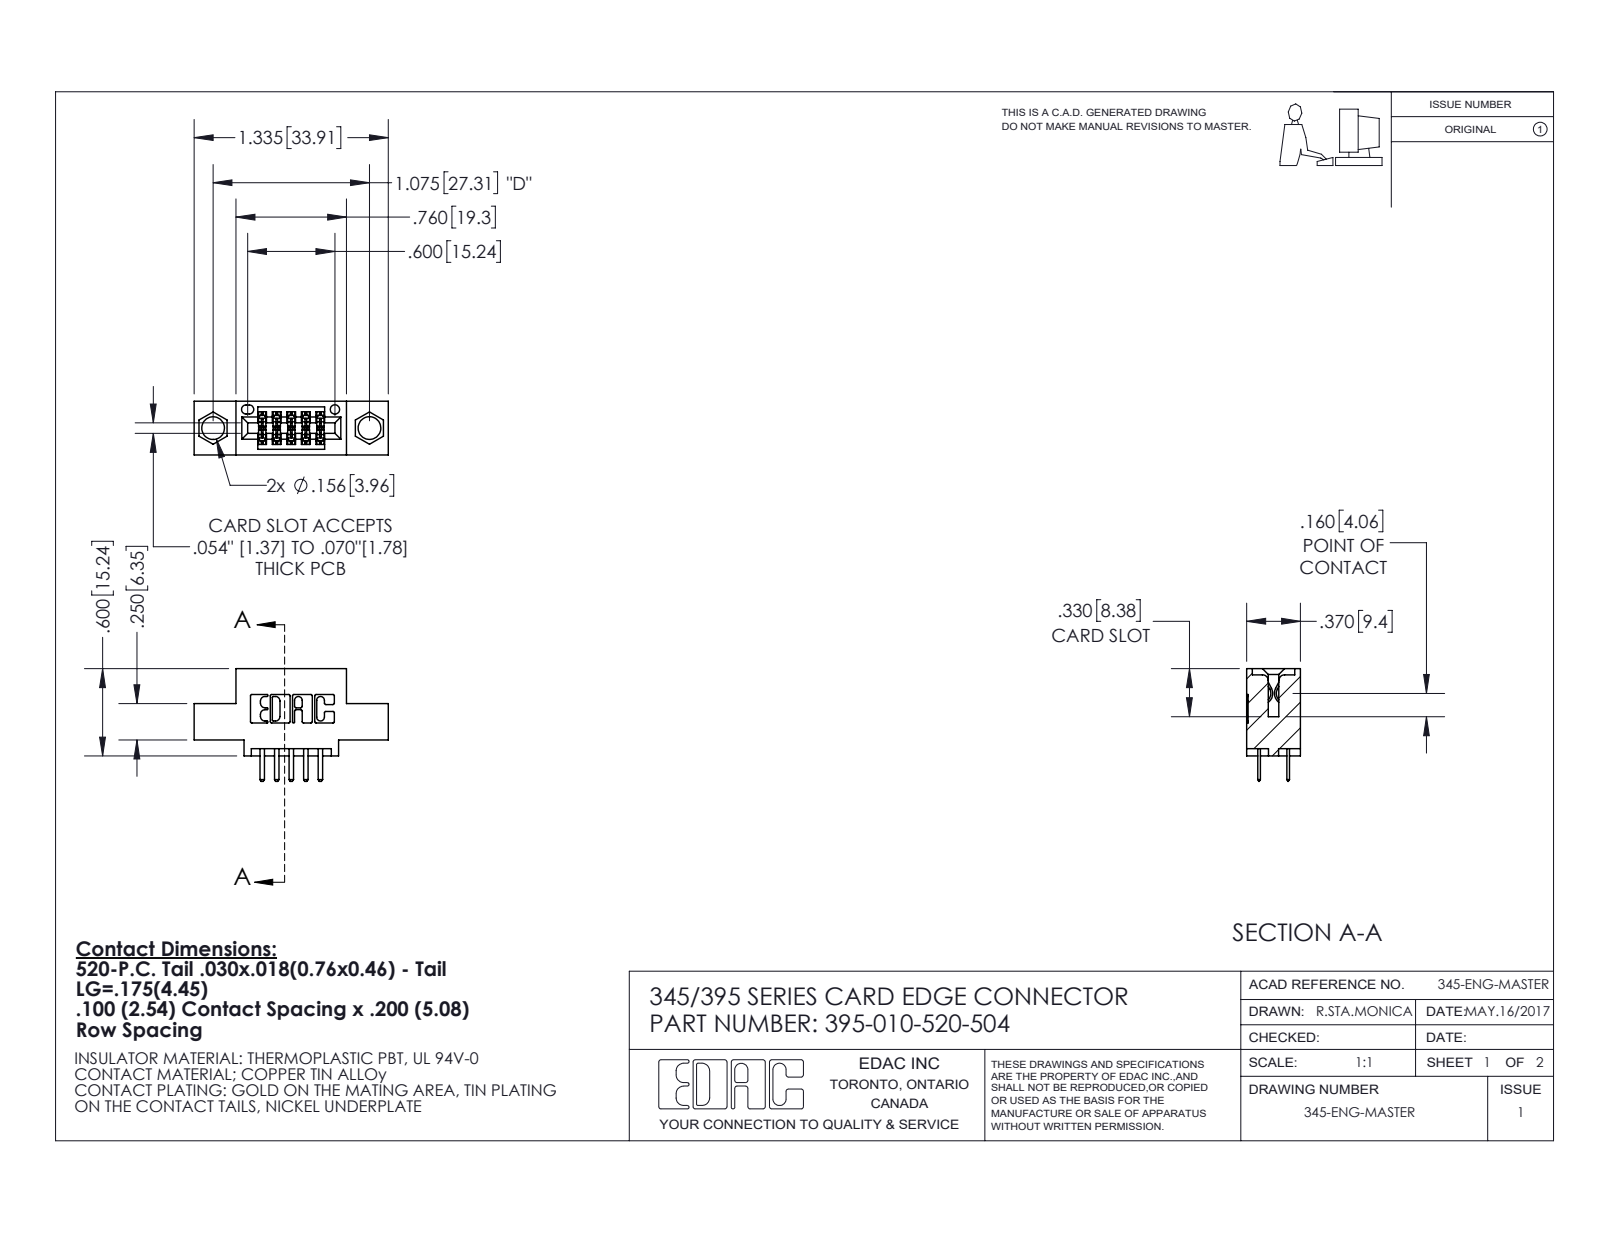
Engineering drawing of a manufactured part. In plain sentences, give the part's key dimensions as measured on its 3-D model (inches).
The part is named "395-010-520-504; 345 Part_0.110 Offset - 0.156 Dia-TI; 345-292-001_345-293-120". Its 3-D file was written by "SolidWorks 2020 (CONFIG_CONTROL_DESIGN)". It is 11 solids with 684 faces: 448 planar, 236 cylindrical and 0 other. Overall it measures 1.335 by 0.775 by 0.37 inches. Its volume is 0.169 cubic inches and its surface area 5.128 square inches. Round holes: 2 of diameter 0.156, 1 of diameter 0.064. Partial cylindrical surfaces (rounded edges, fillets, slot ends): 22 of radius 0.01, 15 of radius 0.006, 14 of radius 0.01, 6 of radius 0.007, 6 of radius 0.031, 3 of radius 0.026, 2 of radius 0.014, 2 of radius 0.019. The main face-to-face distances are 0.2, 0.37, 0.298, 0.072, 0.1, 0.25, 0.025, 0.098, 0.272, 0.06. The hole center spacings are 0.27, 0.847, 1.075.
